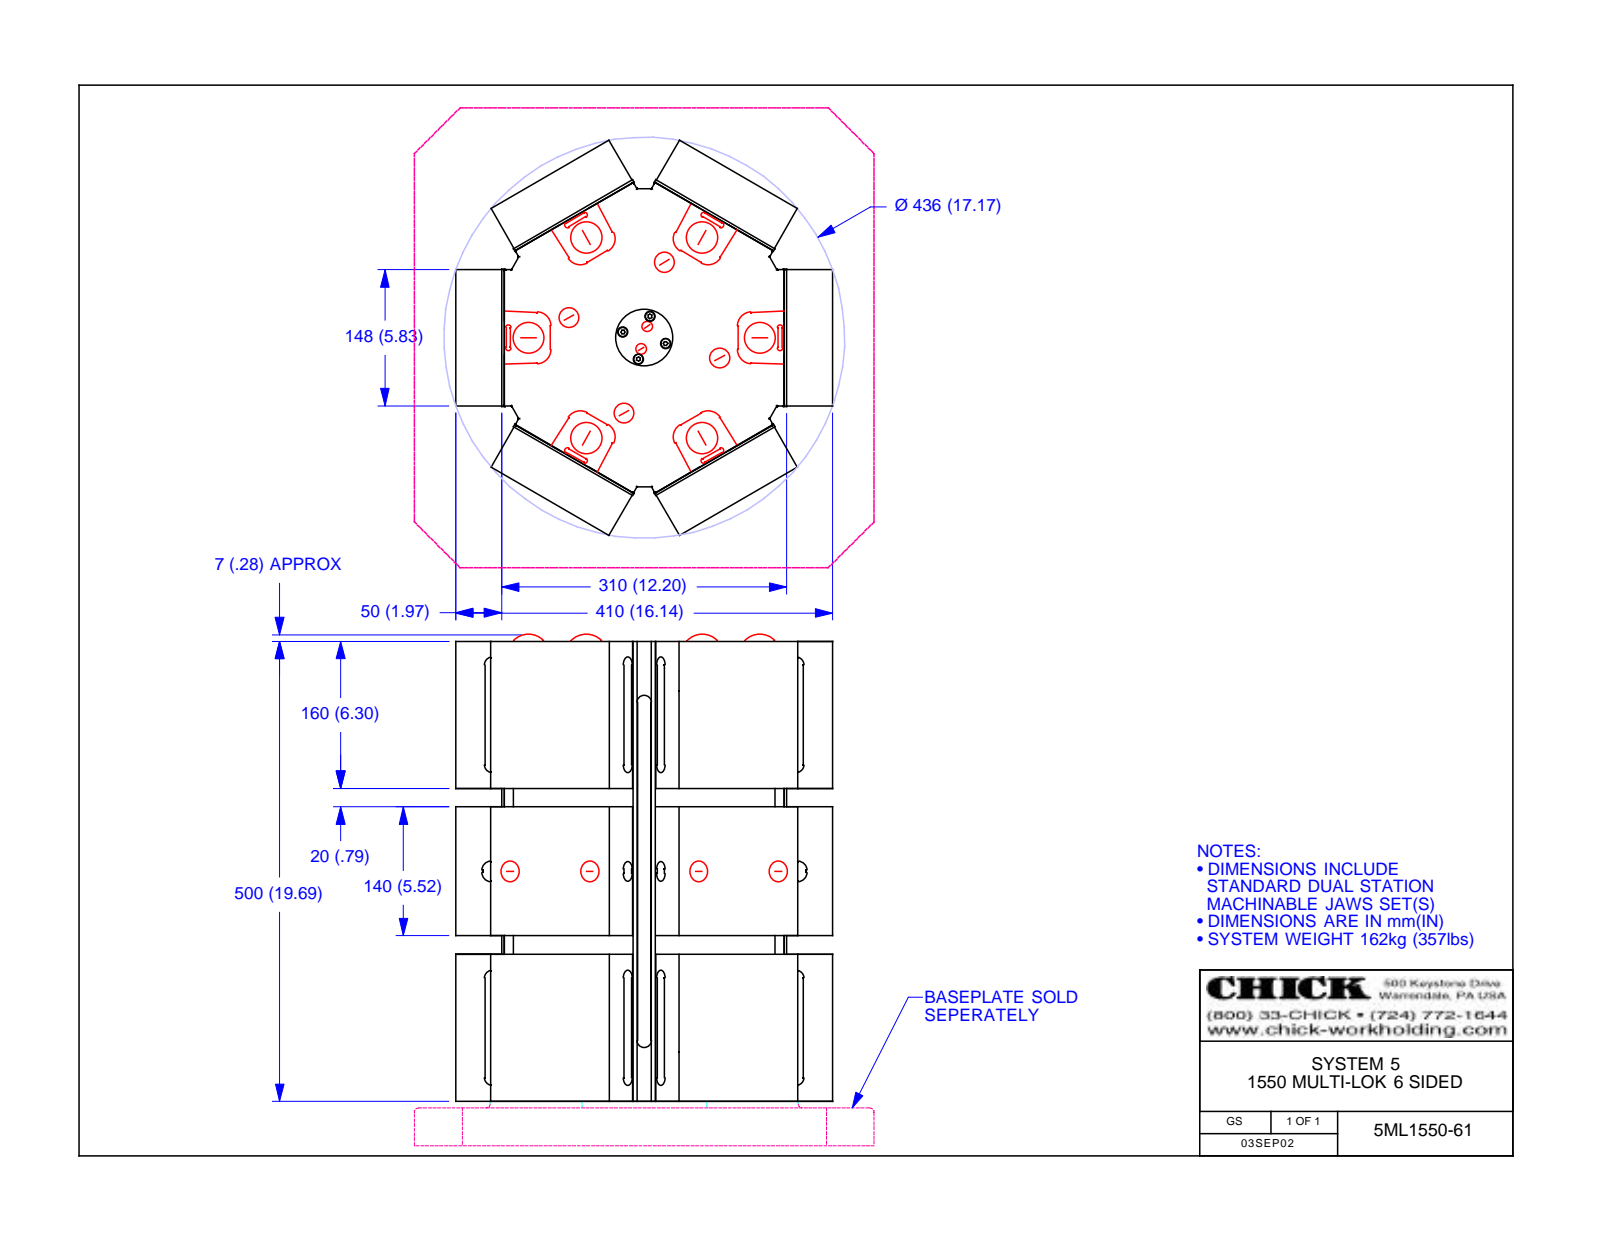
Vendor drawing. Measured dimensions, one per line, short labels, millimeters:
name: 5ML1550-61; 5CLM1550-61; 5CP1550-ST; 5DS1550-15-50 (+2 more)
written by: Autodesk Inventor 2013 (AUTOMOTIVE_DESIGN)
unit: mm
bodies: 25 solids, 9854 faces (7911 planar, 690 cylindrical, 1253 other)
size: 507.2 × 428.01 × 410
volume: 54 320 000 mm³; area: 3 441 000 mm²
holes: 30× ⌀10.33, 30× ⌀11, 30× ⌀18.15, 30× ⌀26.97, 24× ⌀17, 12× ⌀8.65, 12× ⌀10.5, 12× ⌀18, 12× ⌀20, 7× ⌀10, 6× ⌀10.11, 5× ⌀4.06
bosses: 12× ⌀8.5, 5× ⌀7.67, 5× ⌀4.76, 4× ⌀20
rounds: 168× R2, 24× R15.9, 20× R0.4, 20× R1.2, 20× R3, 10× R1.65, 10× R2.83, 10× R7
face distances: 3, 307, 310, 50, 53, 357, 360, 304, 410, 320
hole spacings: 175, 230, 201.56, 100, 201.36, 350, 0.4, 55
